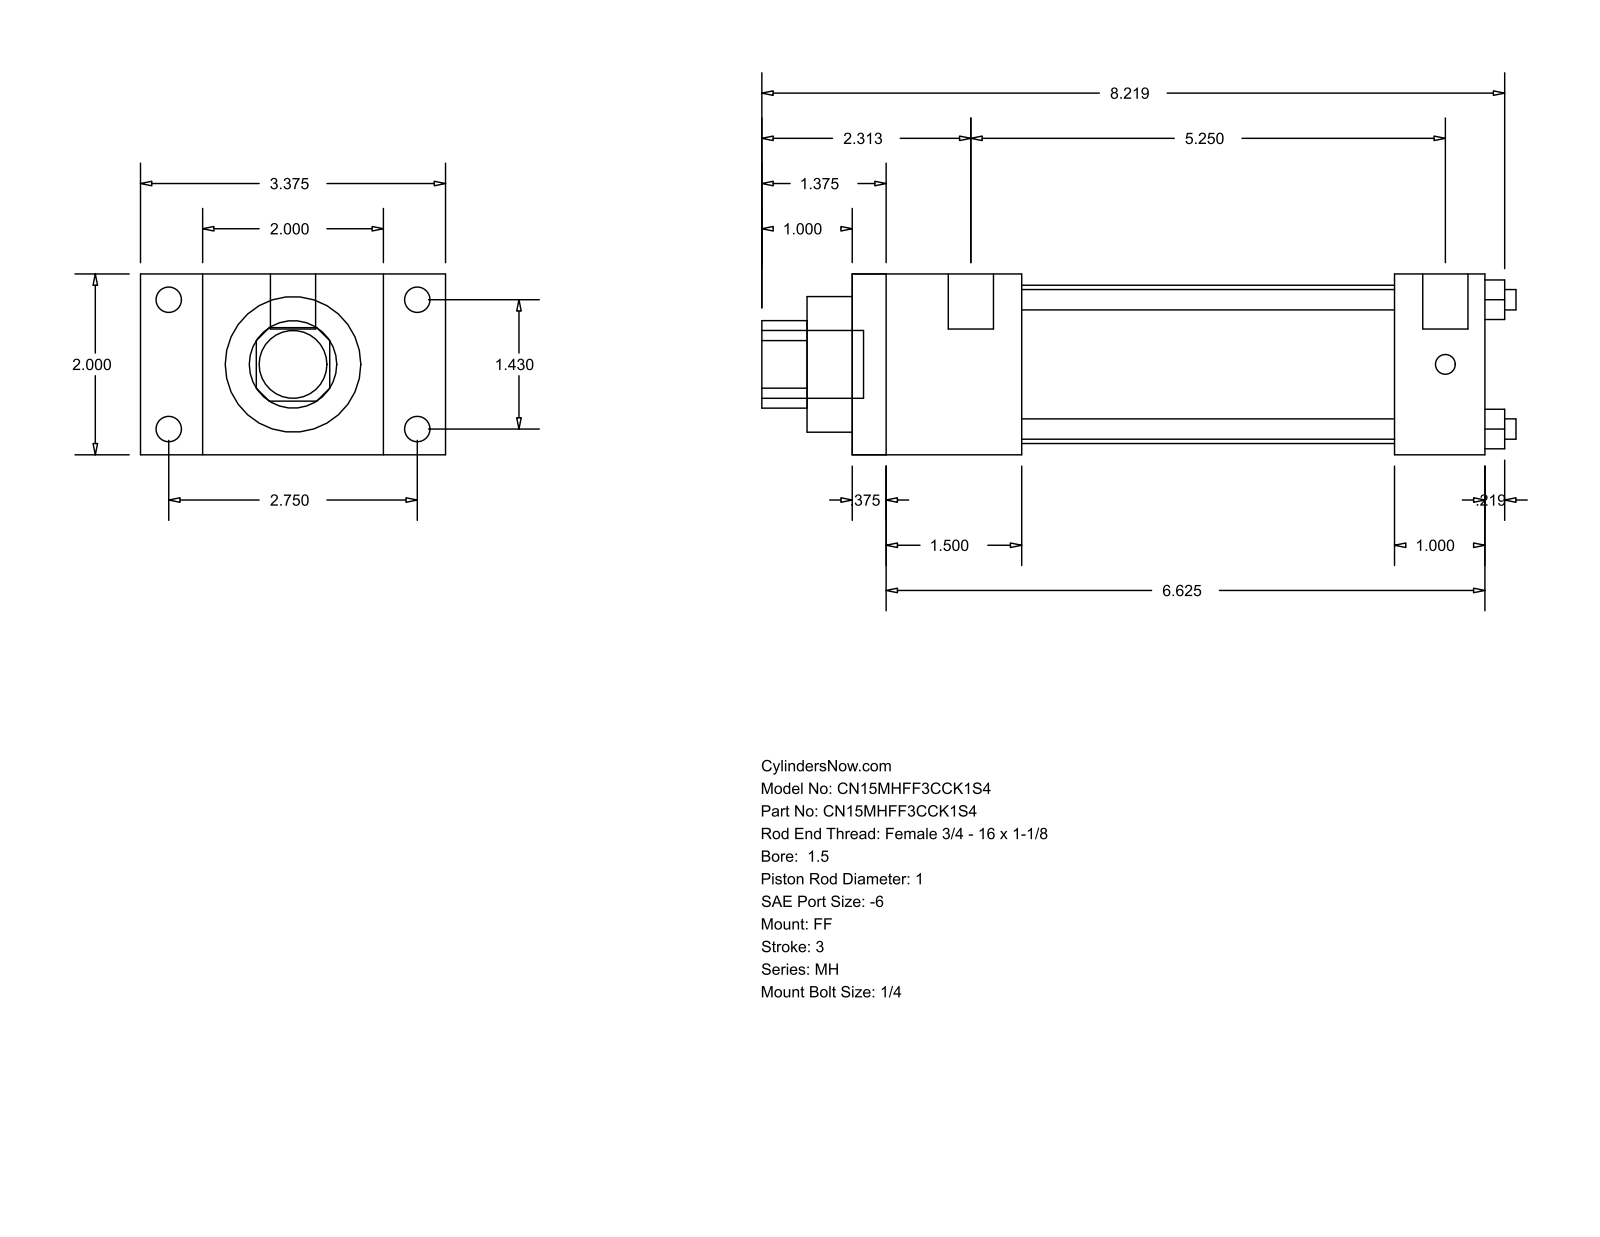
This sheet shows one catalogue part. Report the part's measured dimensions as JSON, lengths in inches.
{"part_name": "MH_FF__0150_1", "step_written_by": "GSSL Pune (CONFIG_CONTROL_DESIGN)", "units": "inches", "bodies": {"solids": 0, "faces": 92, "planar": 64, "cylindrical": 28, "other": 0}, "overall_size": [8.344, 3.375, 2], "round_holes": [[0.225, 4], [1, 1], [1.5, 1], [1.75, 1]], "round_bosses_or_shafts": [[0.281, 4], [0.219, 4], [0.5, 2], [0.75, 1]], "partial_cylinders_radius": [[0.484, 1]], "face_to_face_distances": [2, 7, 0.375, 6.625, 1, 0.687, 2.687, 1.875, 1.5, 5.125], "hole_center_spacings": [1.011, 1.43, 2.022]}
